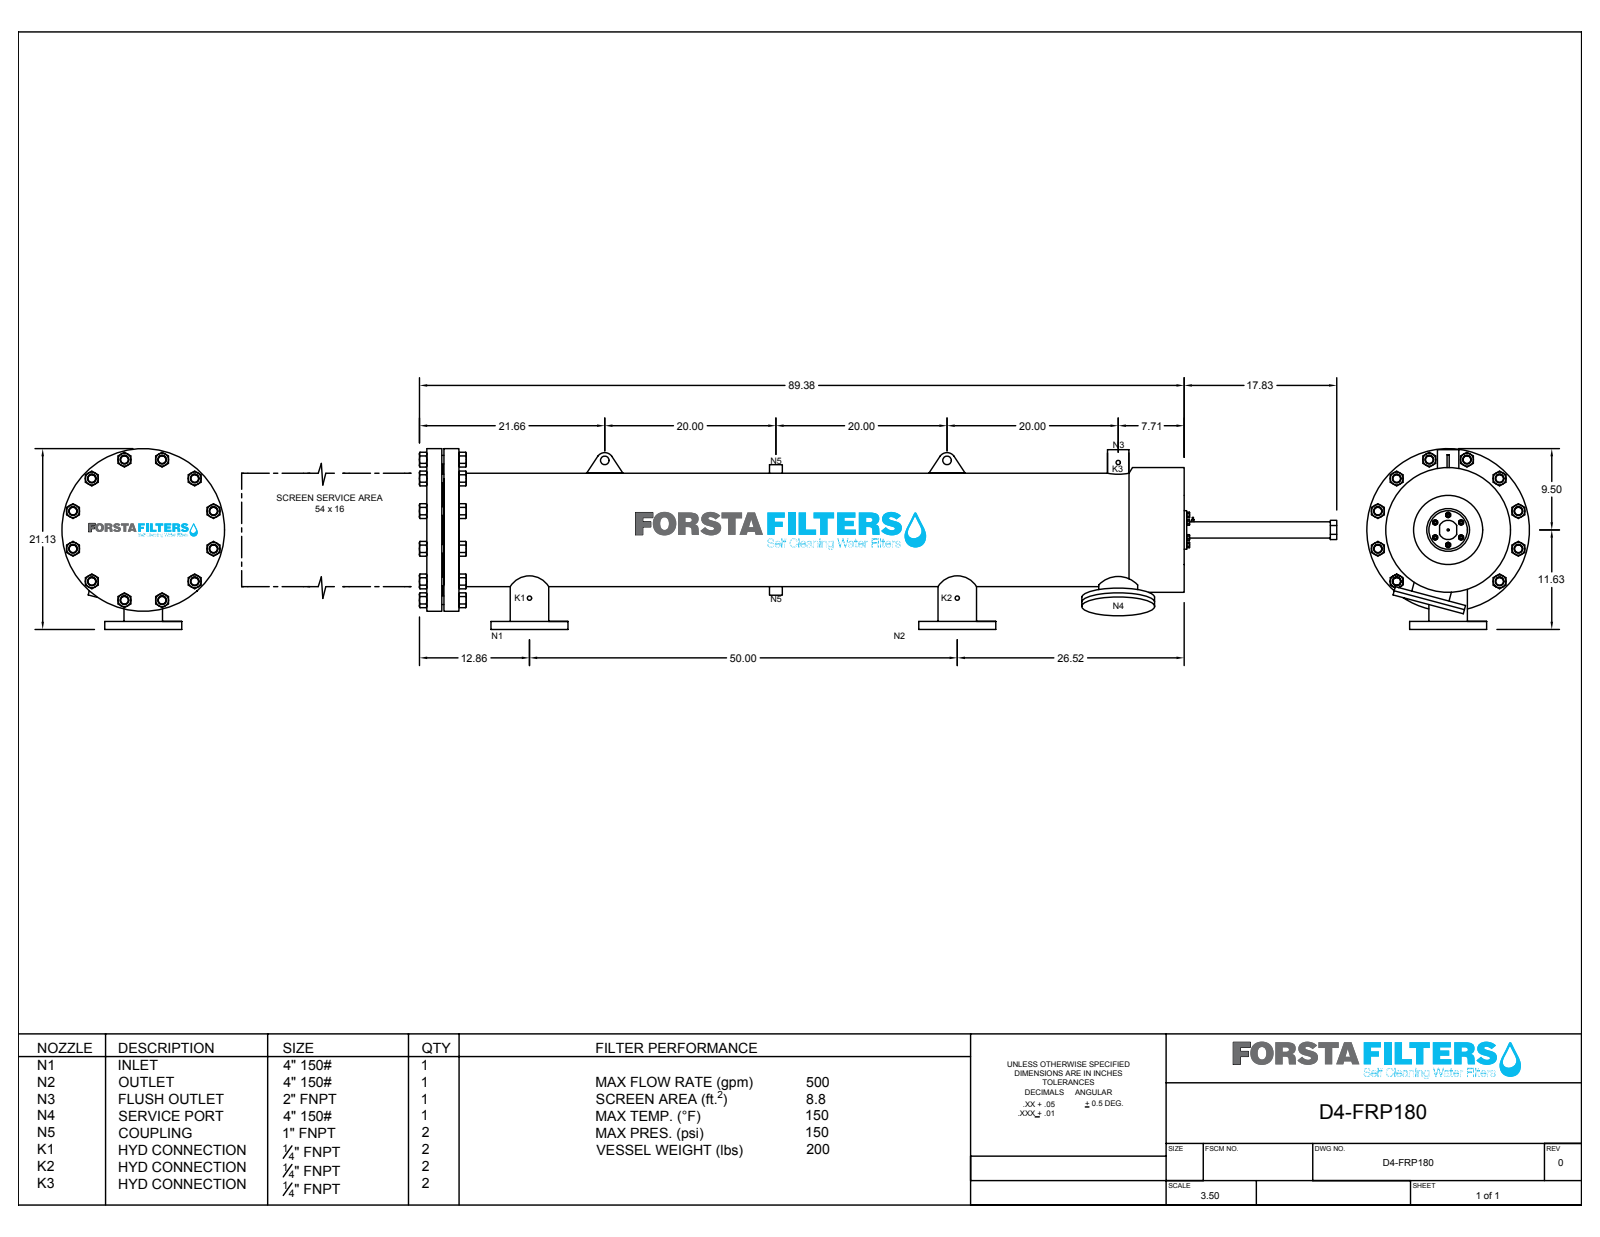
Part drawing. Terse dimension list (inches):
name: D4-FRP-180
written by: SolidWorks 2018 (CONFIG_CONTROL_DESIGN)
unit: in
bodies: 19 solids, 662 faces (296 planar, 342 cylindrical, 24 other)
size: 107.02 × 21.127 × 19
volume: 1 812 in³; area: 10 567 in²
holes: 32× ⌀0.75, 15× ⌀1, 5× ⌀0.375, 4× ⌀0.25, 4× ⌀4, 1× ⌀0.375, 1× ⌀1.506, 1× ⌀12.86, 1× ⌀14.187
bosses: 4× ⌀9, 4× ⌀4.394, 3× ⌀0.644, 1× ⌀19, 1× ⌀14.581, 1× ⌀4.501, 1× ⌀1.901, 1× ⌀1.394
rounds: 2× R1, 1× R1.125
face distances: 2, 0.5, 88.517, 86.517, 88.32, 86.32, 0.197, 1.75, 3.75, 84.57
hole spacings: 2.87, 3.75, 5.303, 6.929, 8.5, 7.5, 9.111, 12.02
